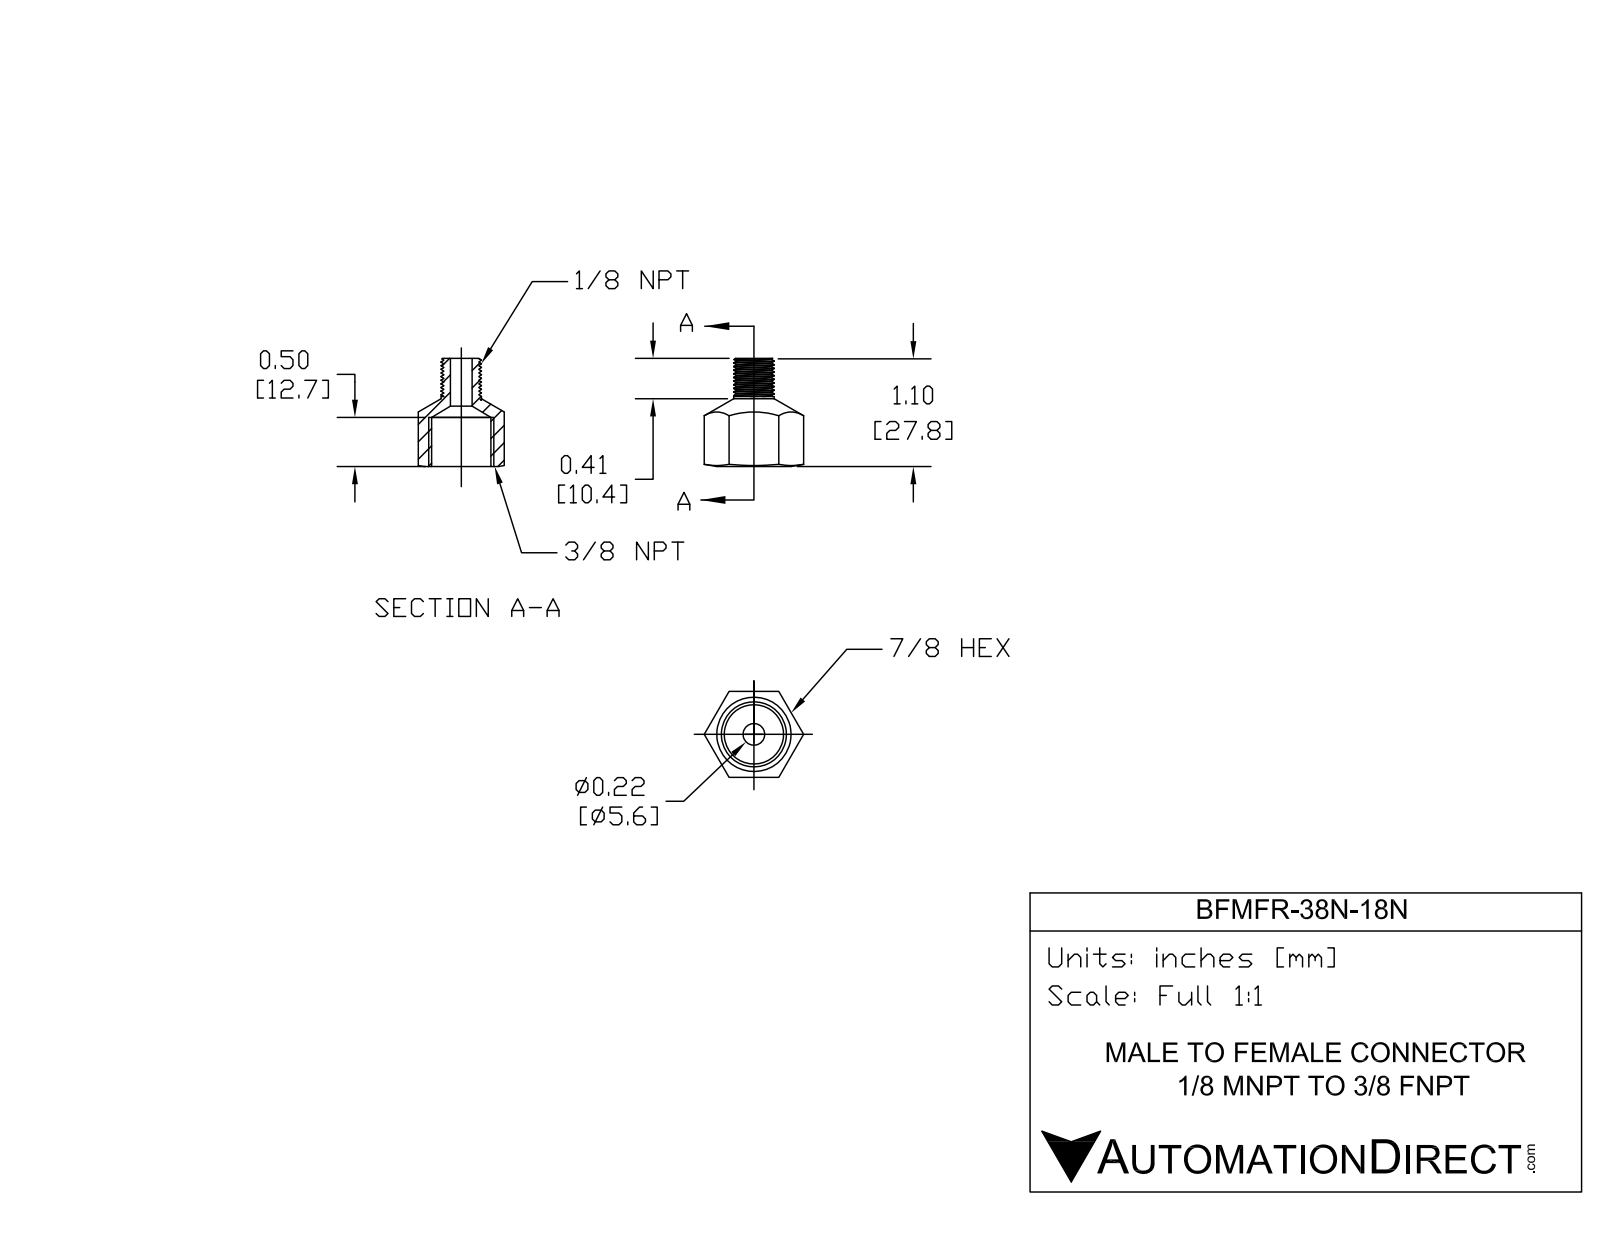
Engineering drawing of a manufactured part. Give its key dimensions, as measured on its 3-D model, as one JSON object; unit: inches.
{"part_name": "BFMFR-38N-18N", "step_written_by": "SolidWorks 2015 (AUTOMOTIVE_DESIGN)", "units": "inches", "bodies": {"solids": 1, "faces": 50, "planar": 11, "cylindrical": 27, "other": 12}, "overall_size": [1.1, 1.01, 0.875], "volume_in3": 0.281, "surface_area_in2": 5.133, "round_holes": [[0.22, 1], [0.603, 1]], "round_bosses_or_shafts": [[0.411, 1], [0.41, 1]], "face_to_face_distances": [0.875, 1.1, 0.713, 0.387, 0.683, 0.03, 0.417]}
